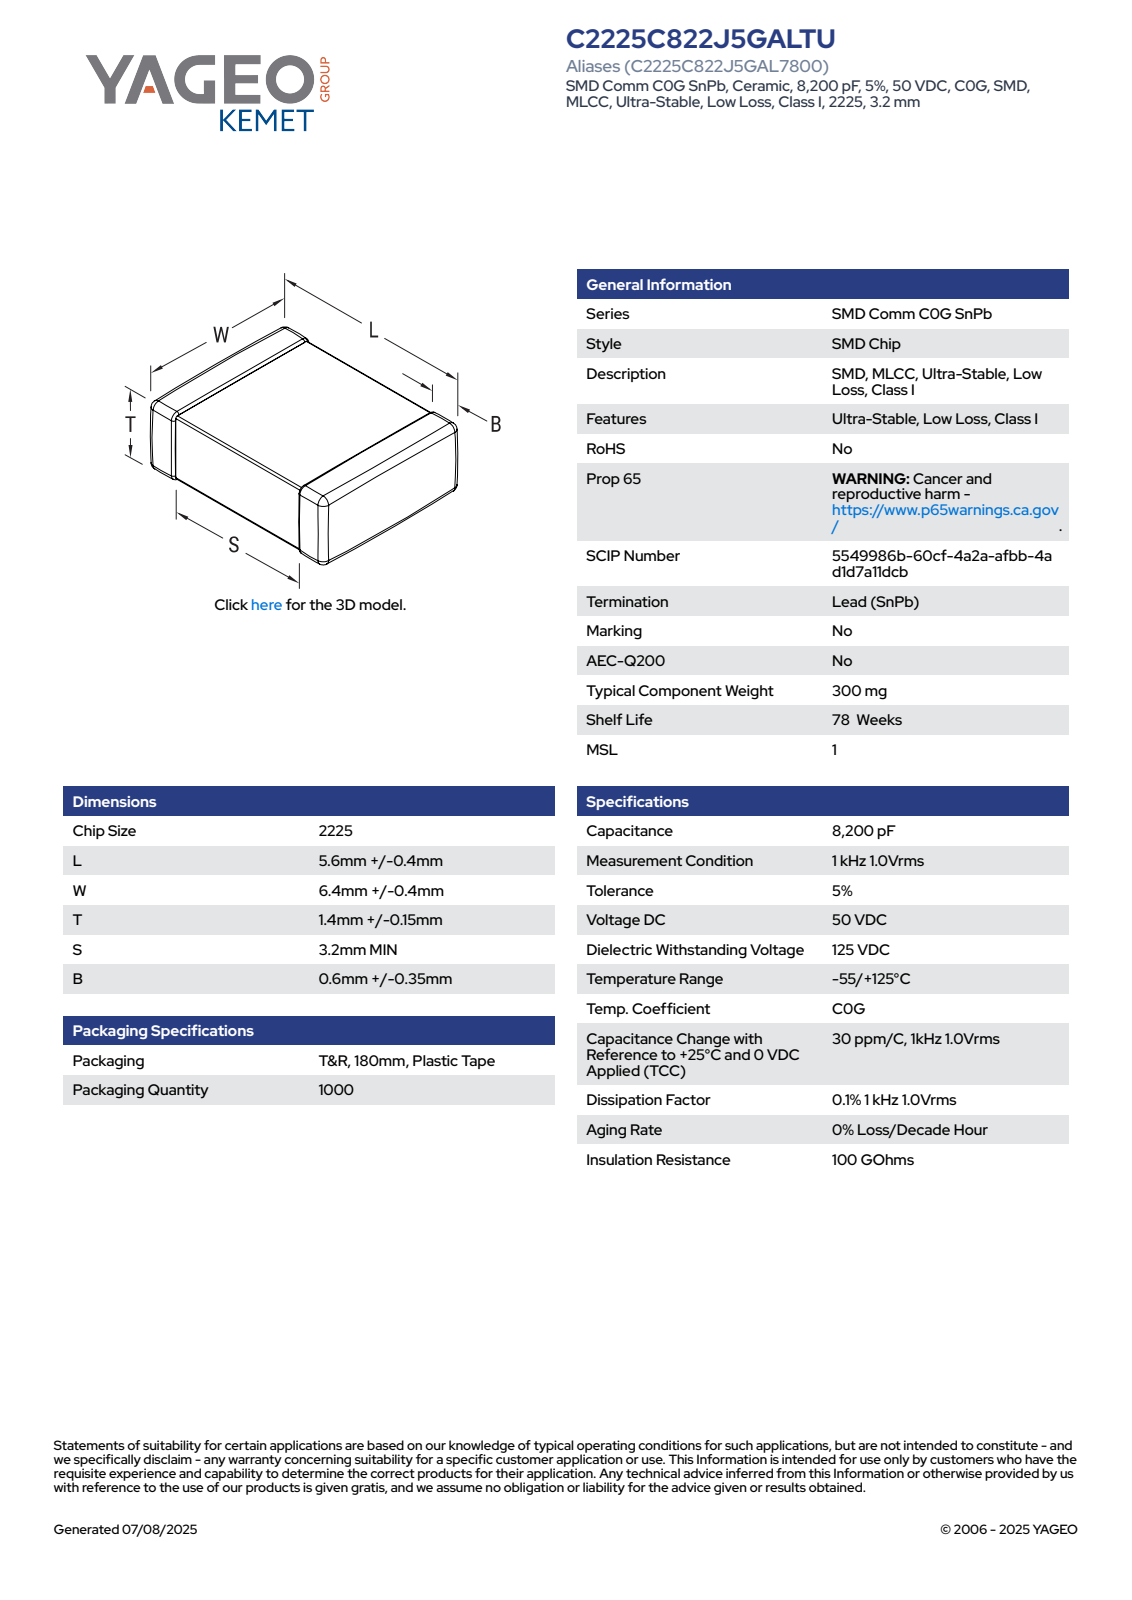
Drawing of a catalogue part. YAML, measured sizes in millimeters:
part_name: "CCS_CCSTDNOS_2225_L6W6.8T1.55B0.95"
step_written_by: "SolidWorks 2014 (AUTOMOTIVE_DESIGN)"
units: millimeters
bodies: {solids: 4, faces: 125, planar: 71, cylindrical: 38, other: 16}
overall_size: [6.8, 6, 1.55]
volume: 54
surface_area: 117
partial_cylinders:
  - {radius: 0.14, count: 24}
face_to_face_distances: [1.27, 1.41, 1.55, 6, 6.52, 6.66, 6.8, 3.33, 0.43, 3.47]
